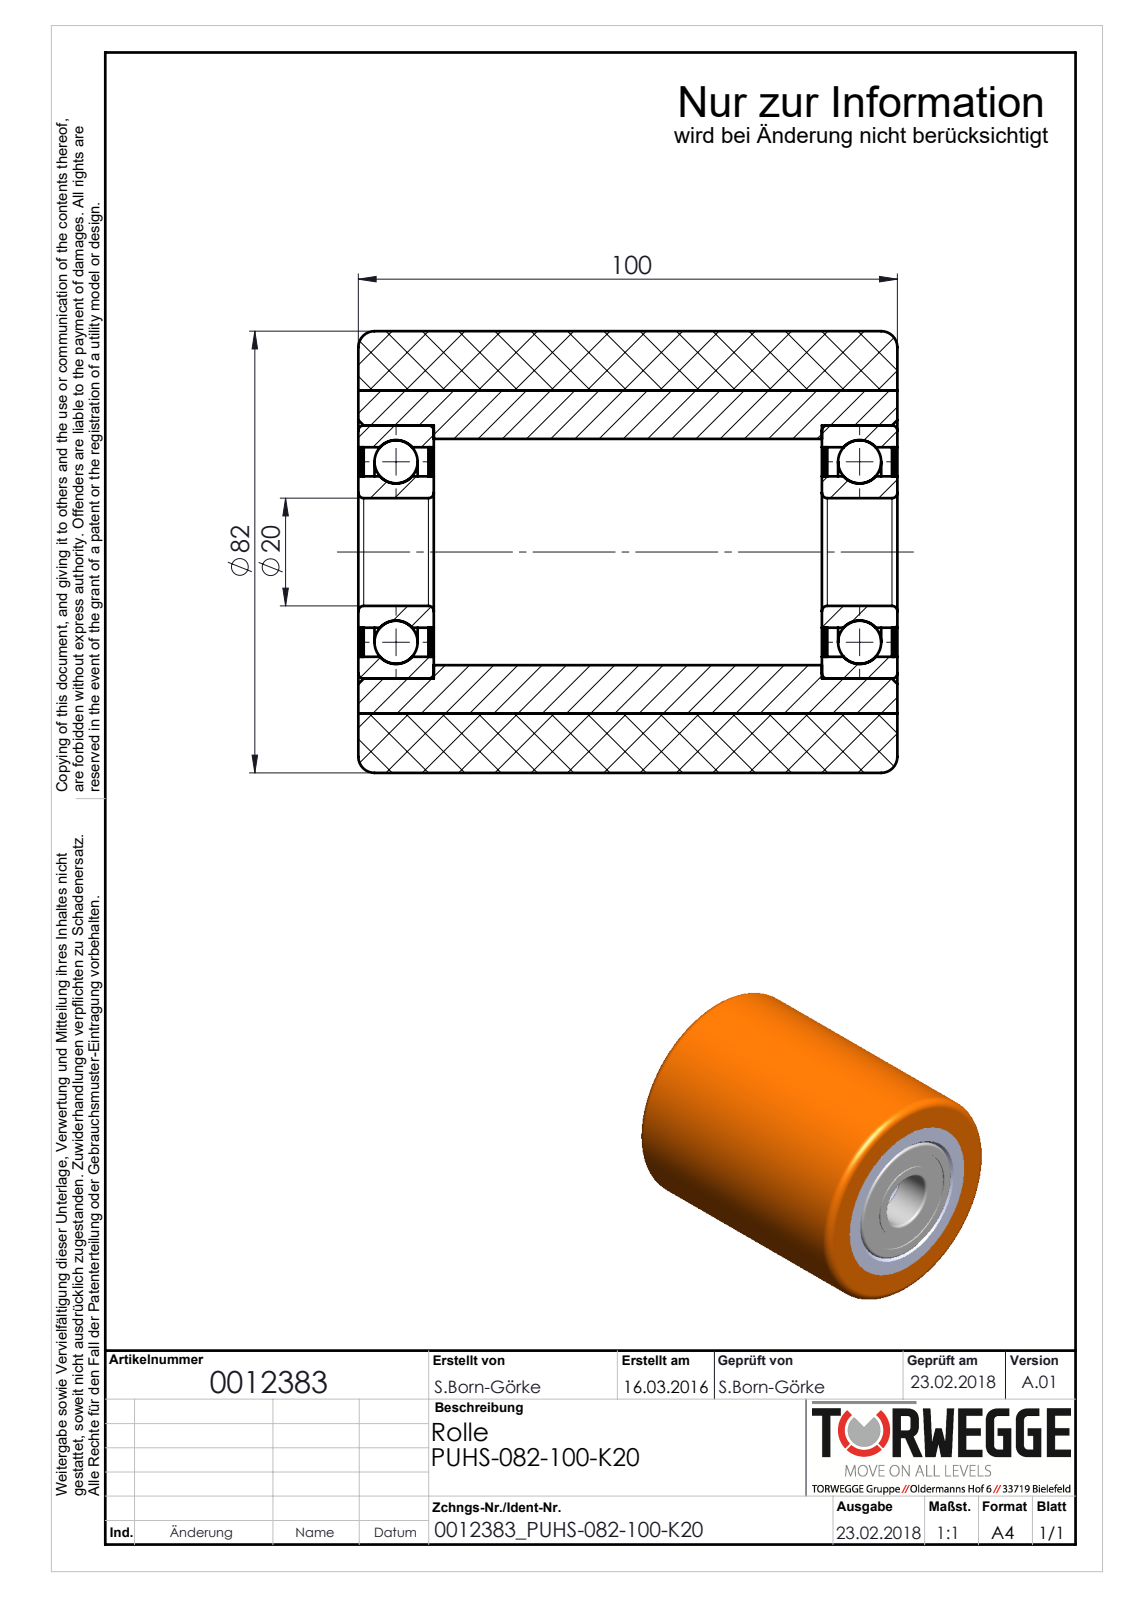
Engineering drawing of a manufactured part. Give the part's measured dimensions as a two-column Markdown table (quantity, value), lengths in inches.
| quantity | value |
| --- | --- |
| part name | 0012383_PUHS-082-100-K20 |
| STEP written by | SolidWorks 2016 (AUTOMOTIVE_DESIGN) |
| units | inches |
| bodies | 12 solids, 118 faces (22 planar, 52 cylindrical, 44 other) |
| overall size | 3.937 × 3.228 × 3.228 |
| volume | 25.11 in³ |
| surface area | 169.7 in² |
| round holes (diameter × count) | 0.787 × 1, 1.106 × 1, 1.531 × 1, 1.654 × 1, 1.85 × 1, 2.362 × 1 |
| round bosses / shafts (diameter × count) | 3.228 × 1 |
| main face-to-face distances | 0.02, 3.386, 0.512, 3.937, 0.039, 0.531, 3.406, 0.492, 3.366, 0.551 |
